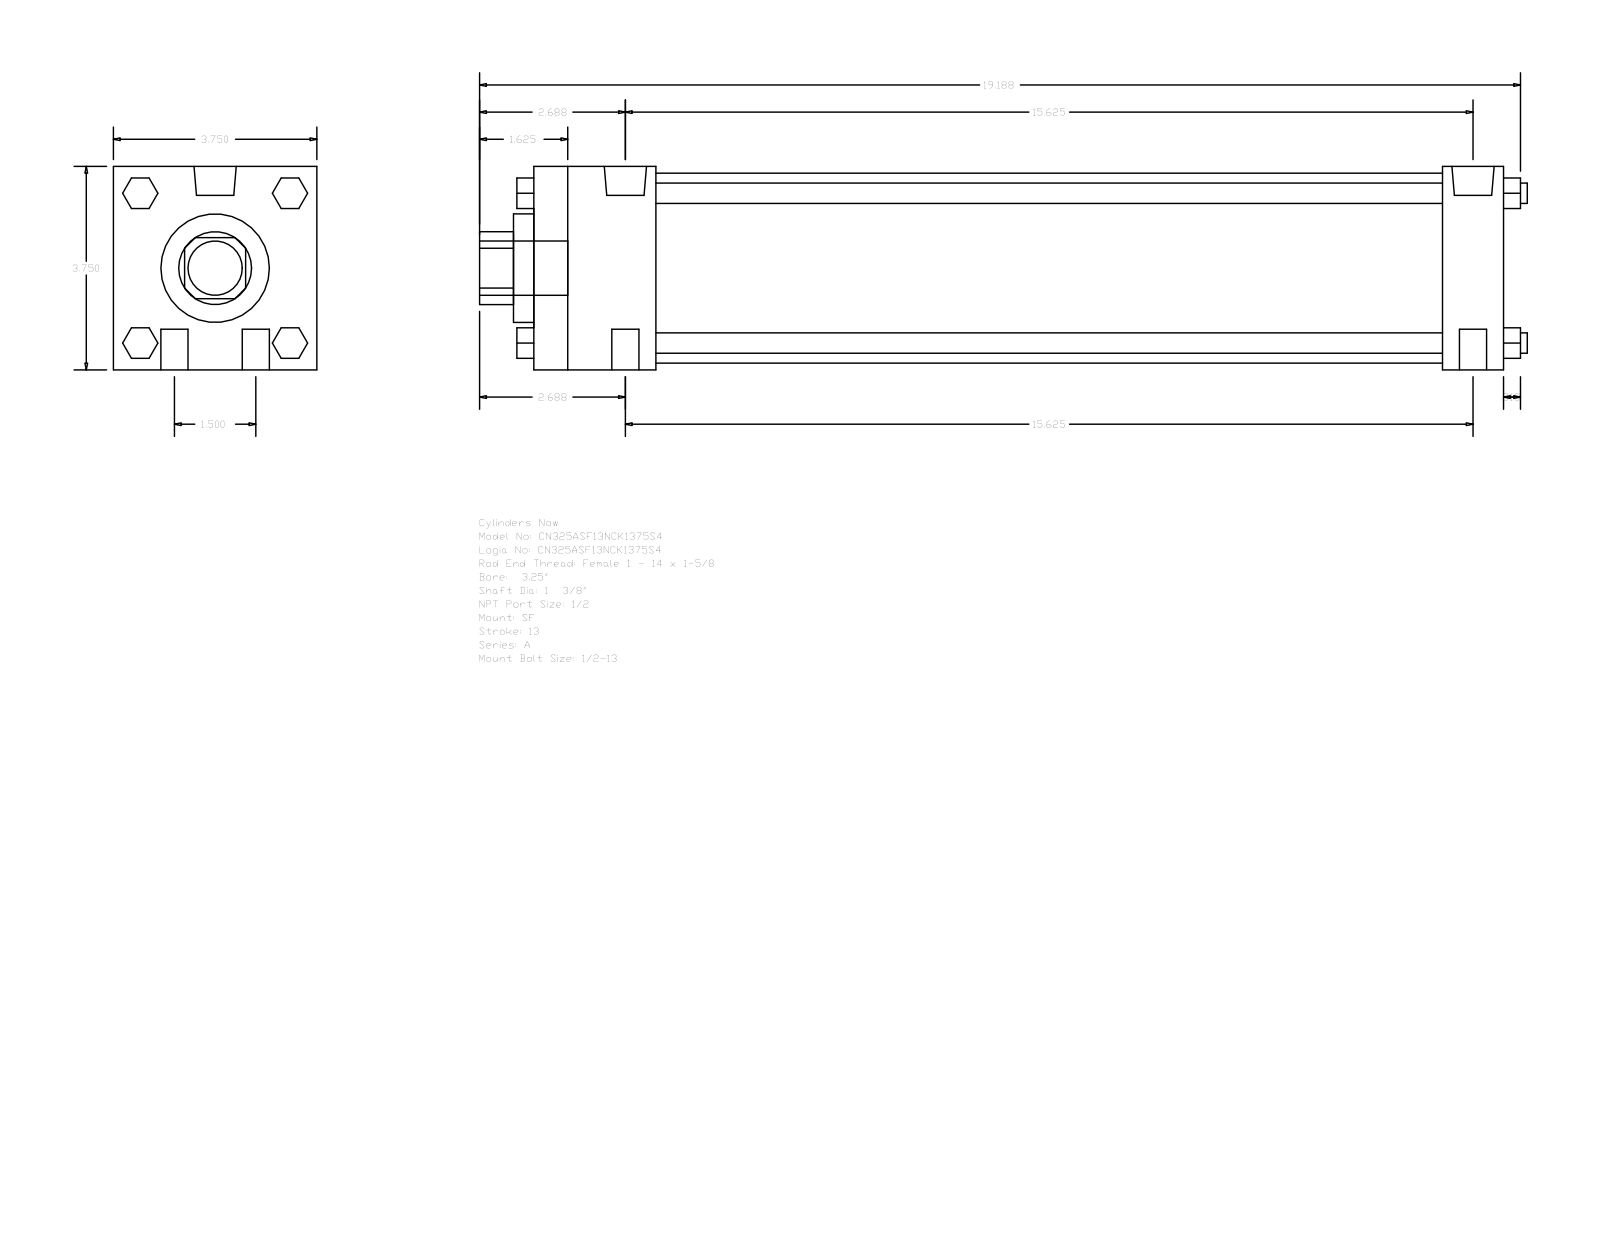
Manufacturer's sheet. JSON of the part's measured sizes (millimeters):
{"part_name": "A_SF__0325_1.375", "step_written_by": "GSSL Pune (CONFIG_CONTROL_DESIGN)", "units": "millimeters", "bodies": {"solids": 0, "faces": 124, "planar": 94, "cylindrical": 30, "other": 0}, "overall_size": [490.54, 95.25, 95.25], "round_holes": [[34.92, 1], [50.8, 1], [88.9, 1]], "round_bosses_or_shafts": [[12.7, 4], [9.53, 4], [19.77, 2], [8.73, 2], [25.4, 1]], "partial_cylinders_radius": [[17.06, 1]], "face_to_face_distances": [95.24, 454.03, 28.58, 425.45, 57.15, 368.3, 396.88, 9.52, 66.67, 434.97]}
